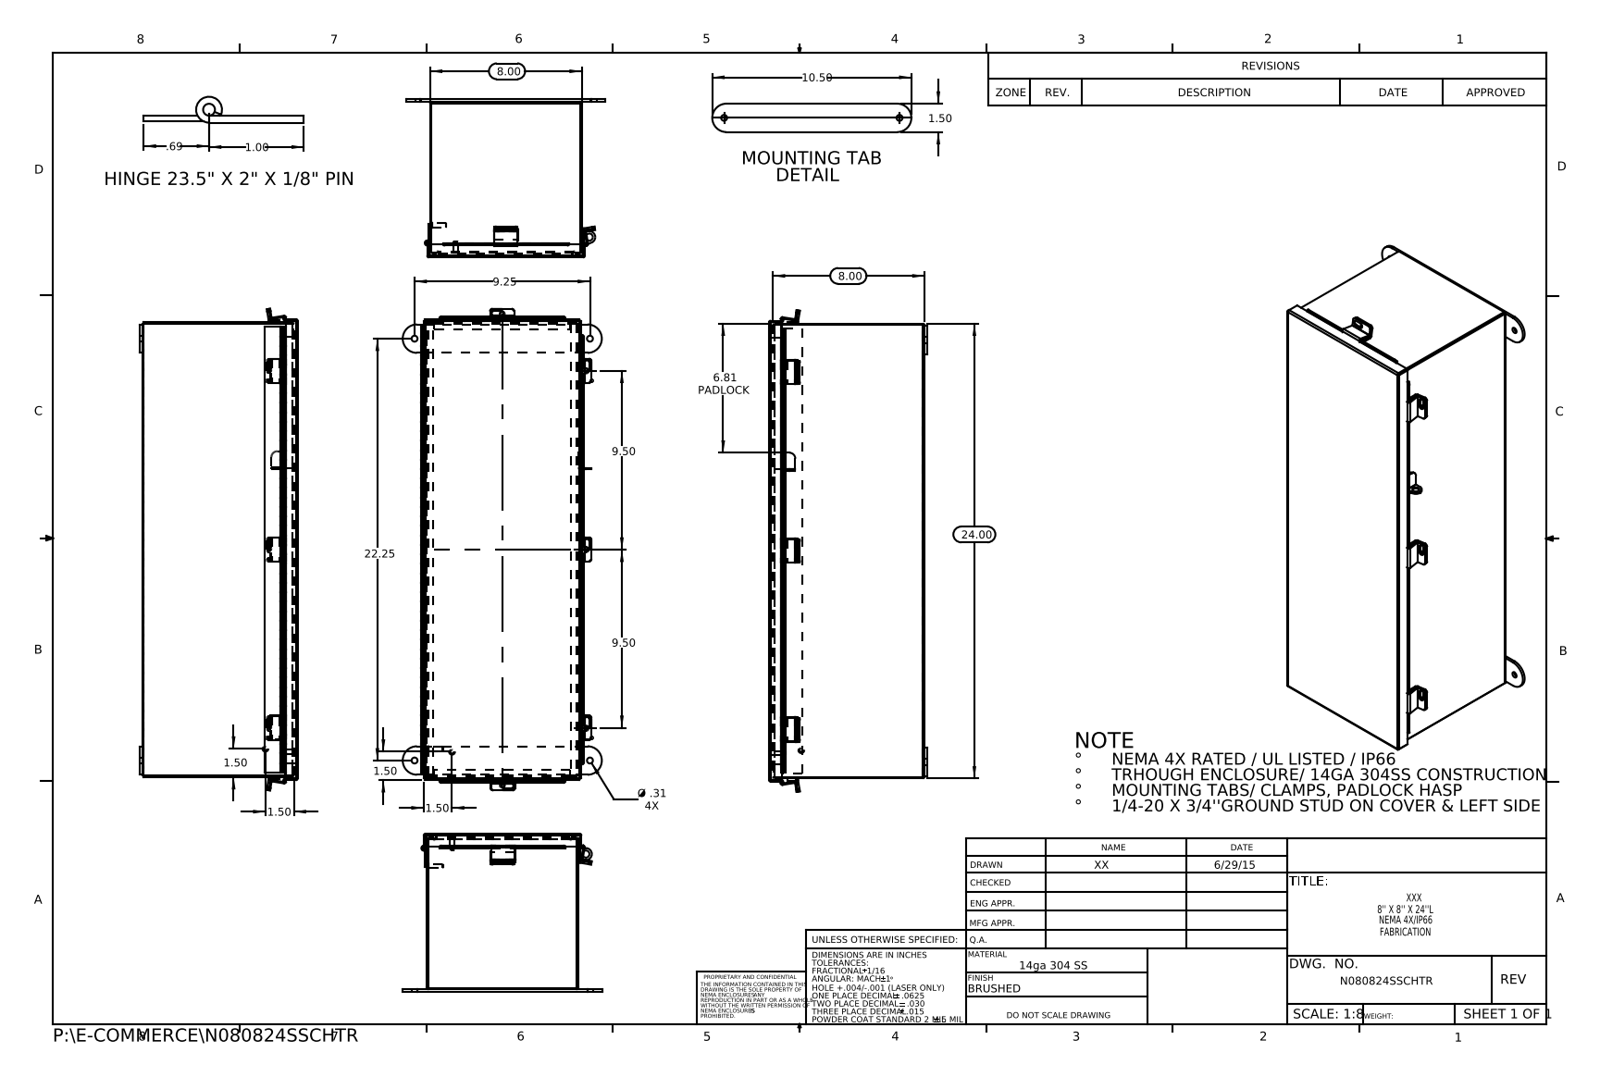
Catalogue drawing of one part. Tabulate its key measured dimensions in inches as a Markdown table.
| quantity | value |
| --- | --- |
| part name | N080824SSCHTR JIC Bottom; HW-CLH-JH-20154; N080824SSCHTR Hinge Body Side; N080824SSCHTR (+8 more) |
| STEP written by | SolidWorks 2015 (CONFIG_CONTROL_DESIGN) |
| units | inches |
| bodies | 21 solids, 886 faces (545 planar, 321 cylindrical, 20 other) |
| overall size | 25.407 × 10.5 × 8.337 |
| volume | 80.2 in³ |
| surface area | 2 140 in² |
| round holes (diameter × count) | 0.25 × 5, 0.313 × 4, 0.125 × 1, 0.375 × 1 |
| round bosses / shafts (diameter × count) | 0.315 × 2, 0.236 × 2, 0.273 × 1, 0.25 × 1 |
| partial cylindrical surfaces (radius × count) | 0.125 × 19, 0.009 × 12, 0.013 × 11, 0.088 × 11, 0.133 × 10, 0.083 × 6, 0.1 × 6, 0.75 × 4 |
| main face-to-face distances | 0.075, 7.925, 8.128, 8, 7.85, 8.203, 8.053, 23.925, 23.85, 24 |
| hole center spacings | 9.25, 9.425, 22.25, 24.096, 8.541, 18.85 |
